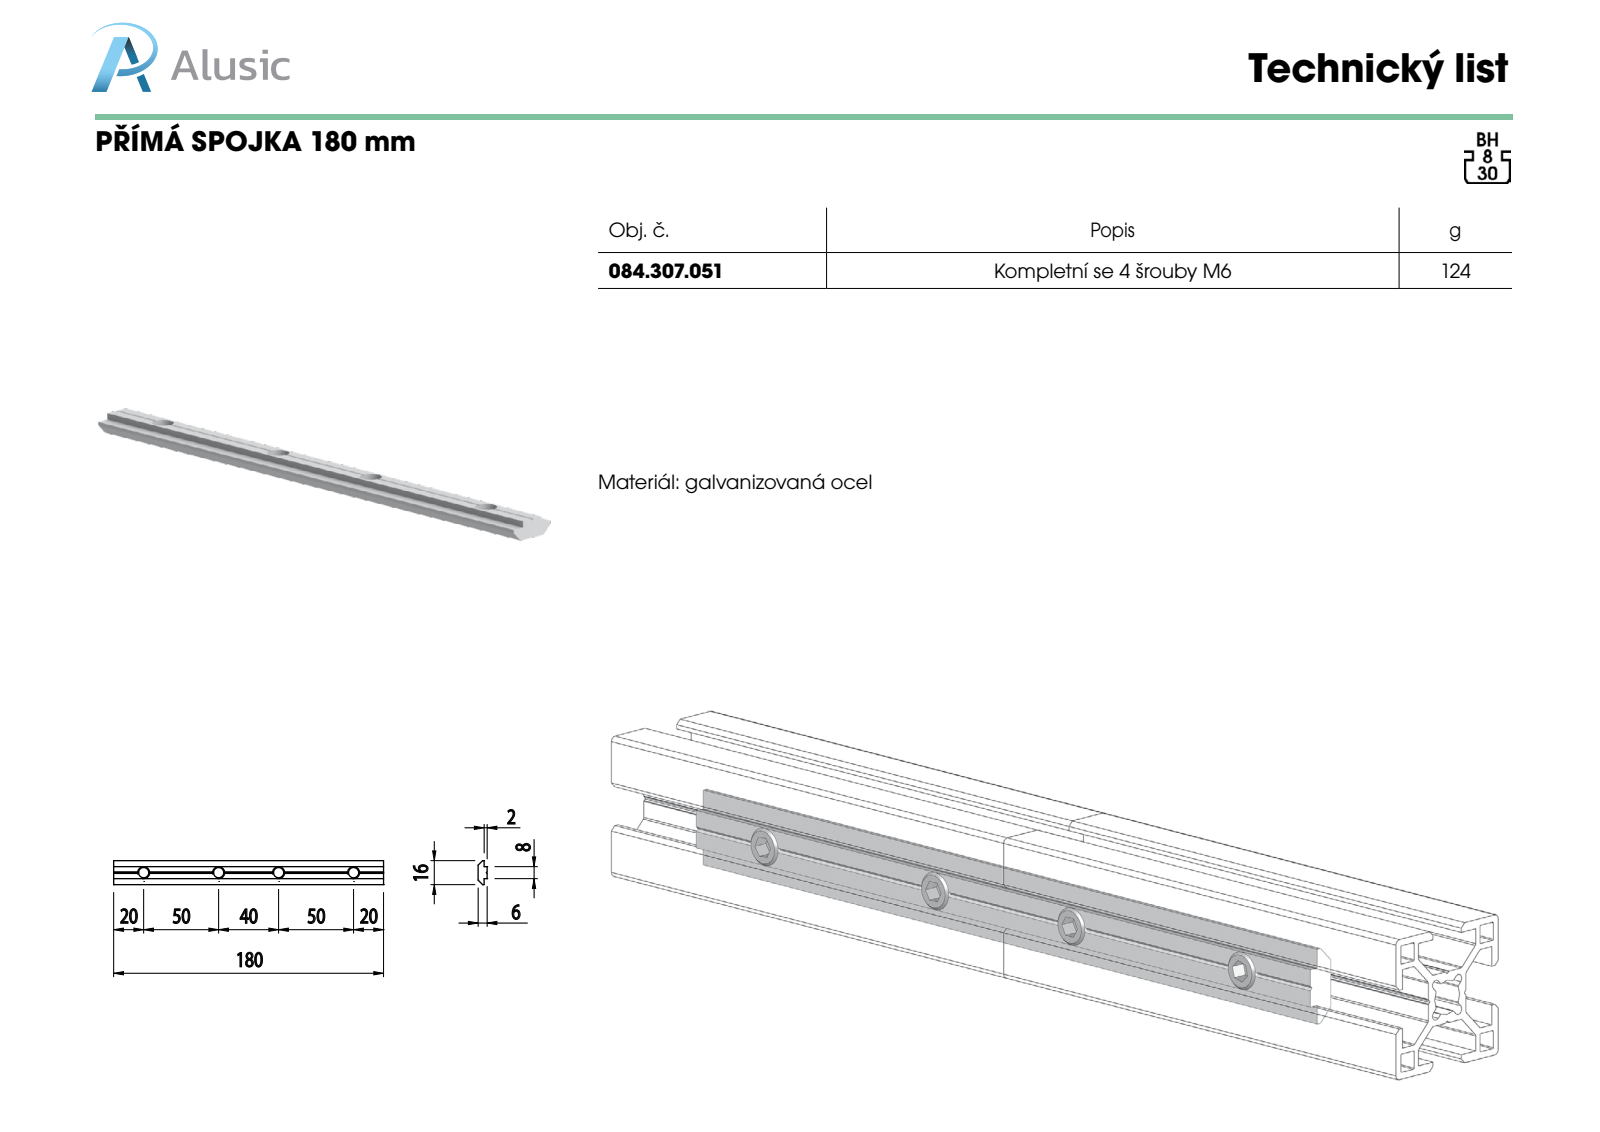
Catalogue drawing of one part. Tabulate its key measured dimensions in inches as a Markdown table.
| quantity | value |
| --- | --- |
| part name | 084.307.051 |
| STEP written by | SolidWorks 2012 (CONFIG_CONTROL_DESIGN) |
| units | inches |
| bodies | 1 solid, 31 faces (23 planar, 8 cylindrical, 0 other) |
| overall size | 7.087 × 0.63 × 0.236 |
| volume | 0.724 in³ |
| surface area | 11.95 in² |
| round holes (diameter × count) | 0.268 × 4 |
| main face-to-face distances | 0.157, 0.236, 0.079, 0.472, 0.315, 0.293, 0.63, 7.087 |
| hole center spacings | 1.969, 3.543, 1.575, 5.512 |
